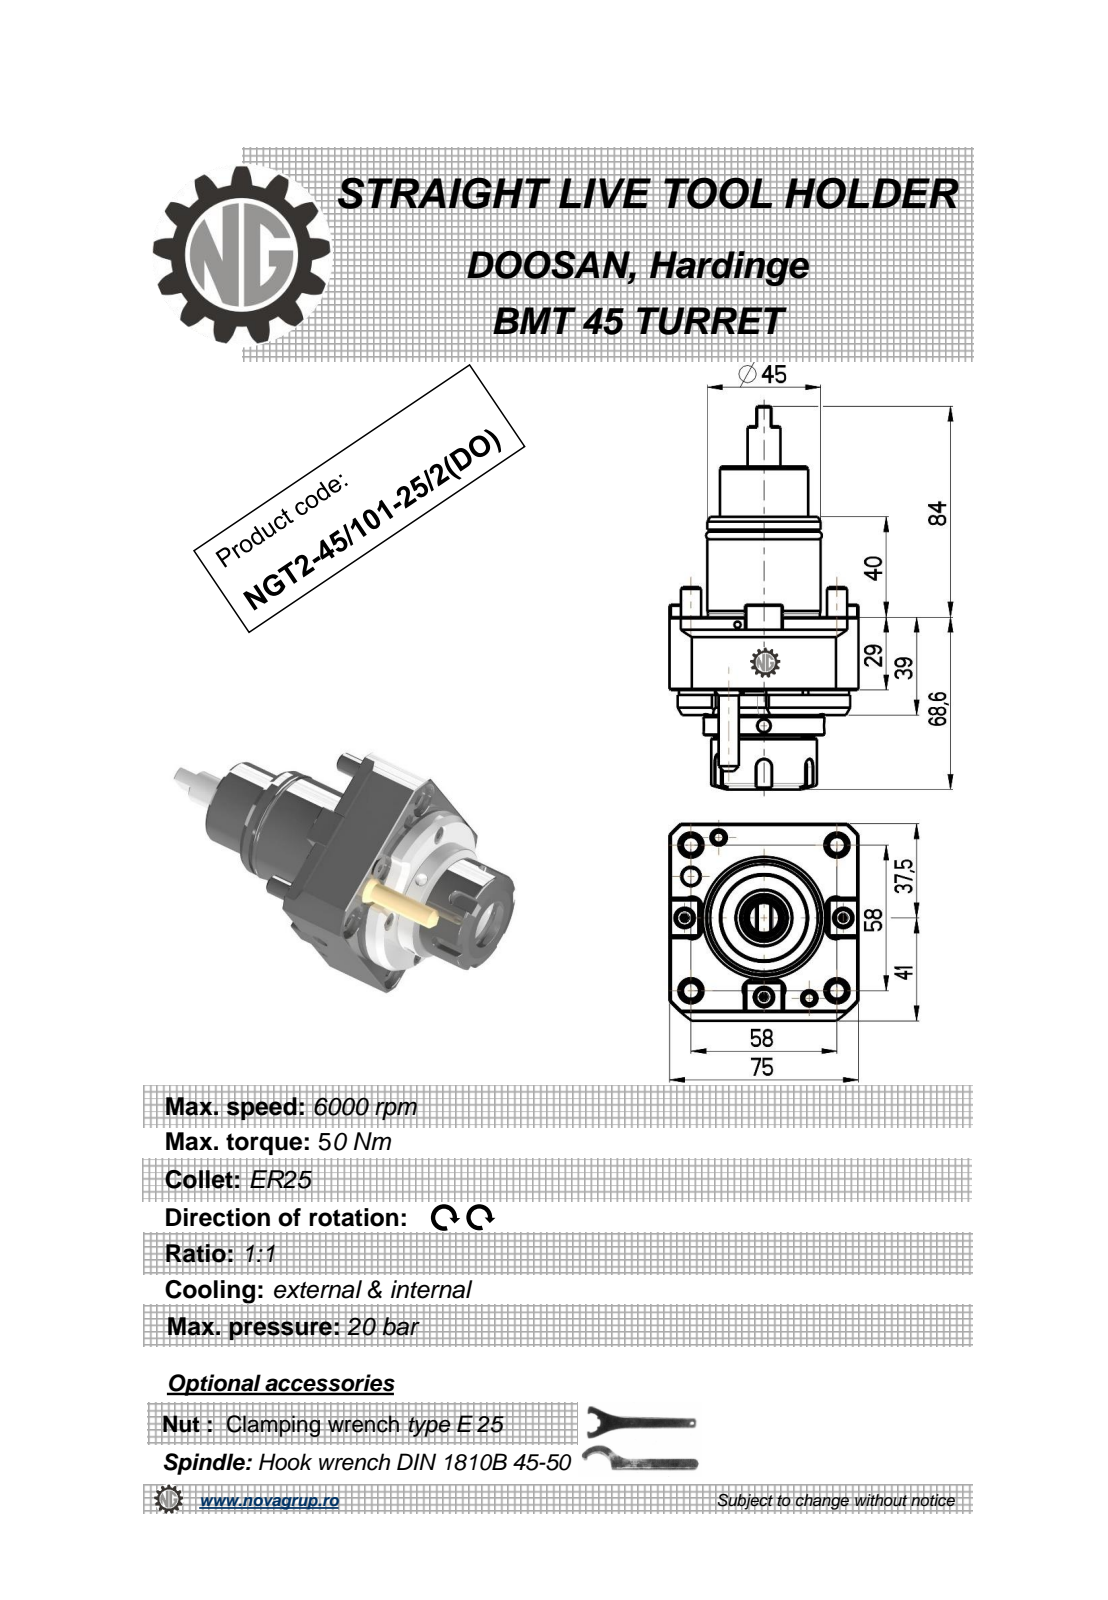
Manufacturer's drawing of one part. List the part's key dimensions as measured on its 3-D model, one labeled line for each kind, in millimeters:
Part name (STEP PRODUCT): NGT2_45_101_25_1_DO
STEP written by: PRO/ENGINEER BY PARAMETRIC TECHNOLOGY CORPORATION, 2010280 (CONFIG_CONTROL_DESIGN)
Units: millimetres
Bodies: 2 solids, 291 faces (118 planar, 69 cylindrical, 104 other)
Overall size (bounding box): 152.6 × 78.5 × 75
Volume: 332 219 mm³ · Surface area: 43 142 mm²
Round holes (diameter × count): ⌀5 ×3, ⌀3 ×1, ⌀6.8 ×1, ⌀20.3 ×1
Round bosses / shafts (diameter × count): ⌀8 ×5, ⌀68.5 ×1, ⌀48 ×1, ⌀45 ×1, ⌀44.4 ×1, ⌀42 ×1, ⌀40 ×1, ⌀35 ×1
Partial cylindrical surfaces — rounded edges, fillets, slot ends (radius × count): R0.2 ×6, R3 ×5, R0.8 ×2, R6 ×2, R33.75 ×1, R50 ×1
Main face-to-face distances: 29, 75, 39, 10, 78.5, 60, 10.5, 18, 0.5, 7.5
Hole centre spacings: 33.11, 33.37, 48.86
